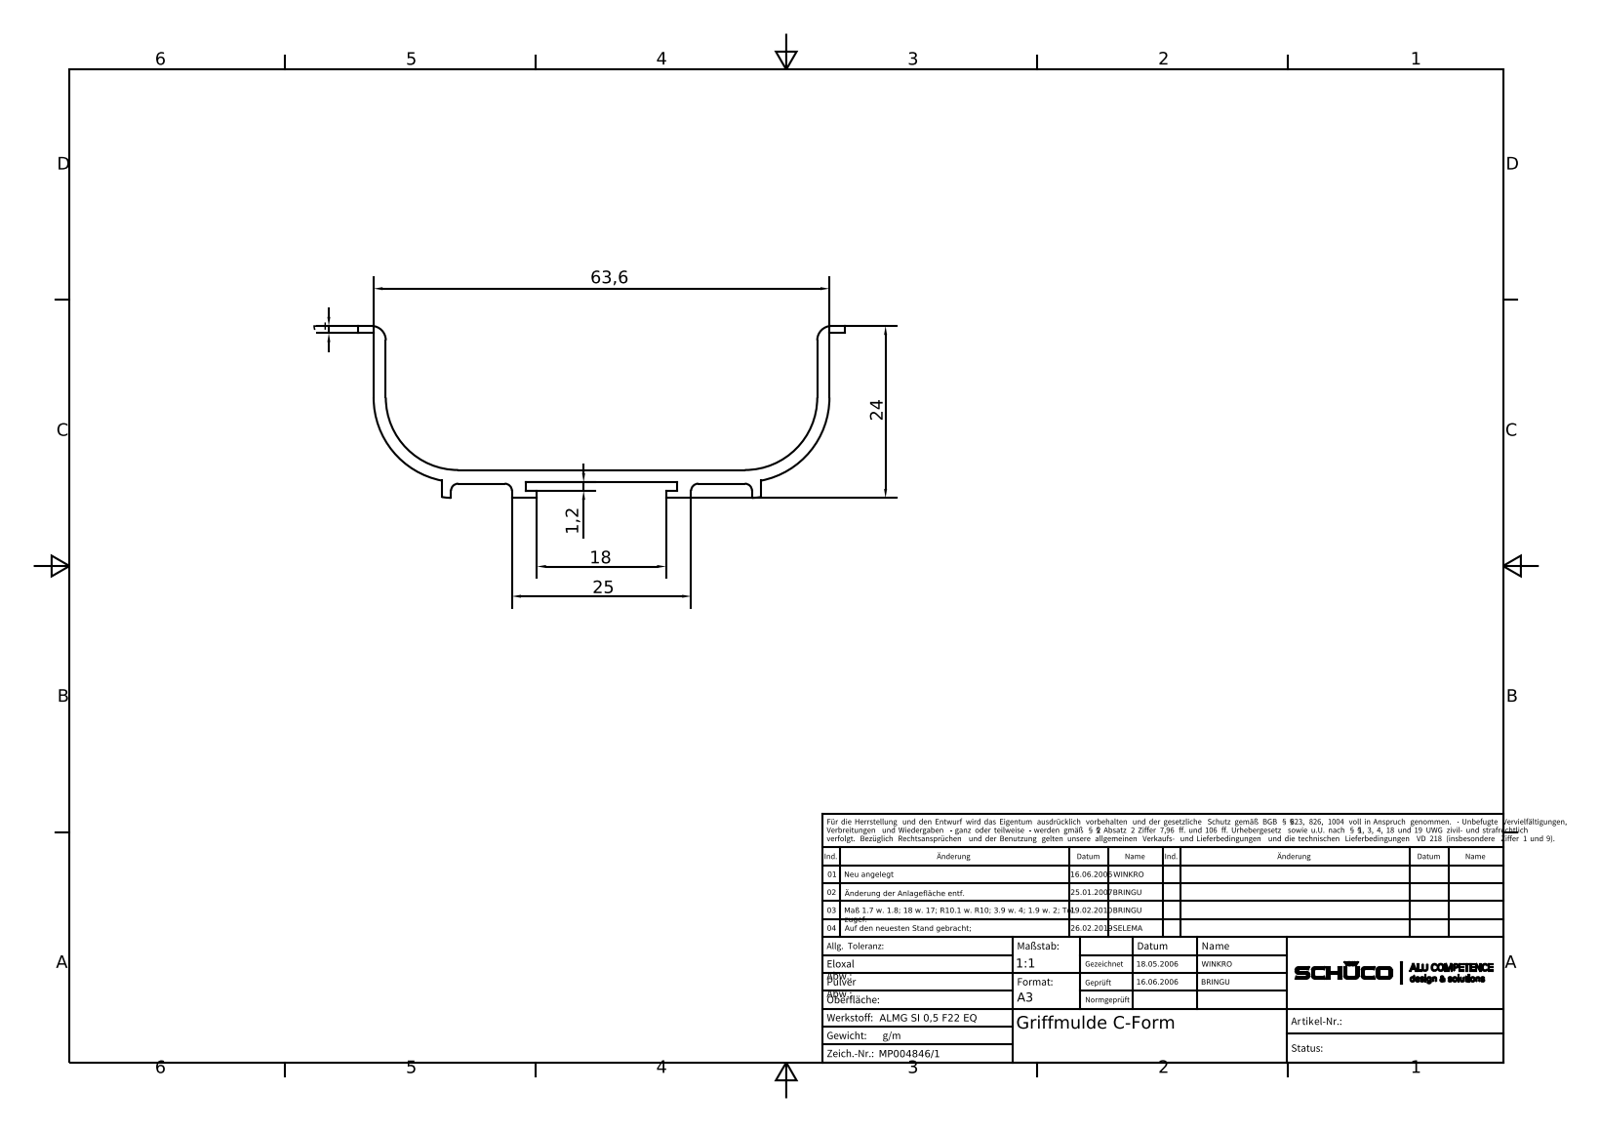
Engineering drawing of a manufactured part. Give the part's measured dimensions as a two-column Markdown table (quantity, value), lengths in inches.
| quantity | value |
| --- | --- |
| part name | MP00484601 |
| STEP written by | Autodesk Inventor 2015 (AUTOMOTIVE_DESIGN) |
| units | inches |
| bodies | 1 solid, 42 faces (30 planar, 12 cylindrical, 0 other) |
| overall size | 2.677 × 0.945 × 0.394 |
| volume | 0.113 in³ |
| surface area | 3.991 in² |
| partial cylindrical surfaces (radius × count) | 0.039 × 4, 0.079 × 2, 0.398 × 2, 0.465 × 2, 0.472 × 2 |
| main face-to-face distances | 0.067, 0.394, 2.437, 0.075, 0.039, 0.906, 0.079, 0.087, 0.154, 2.504 |
